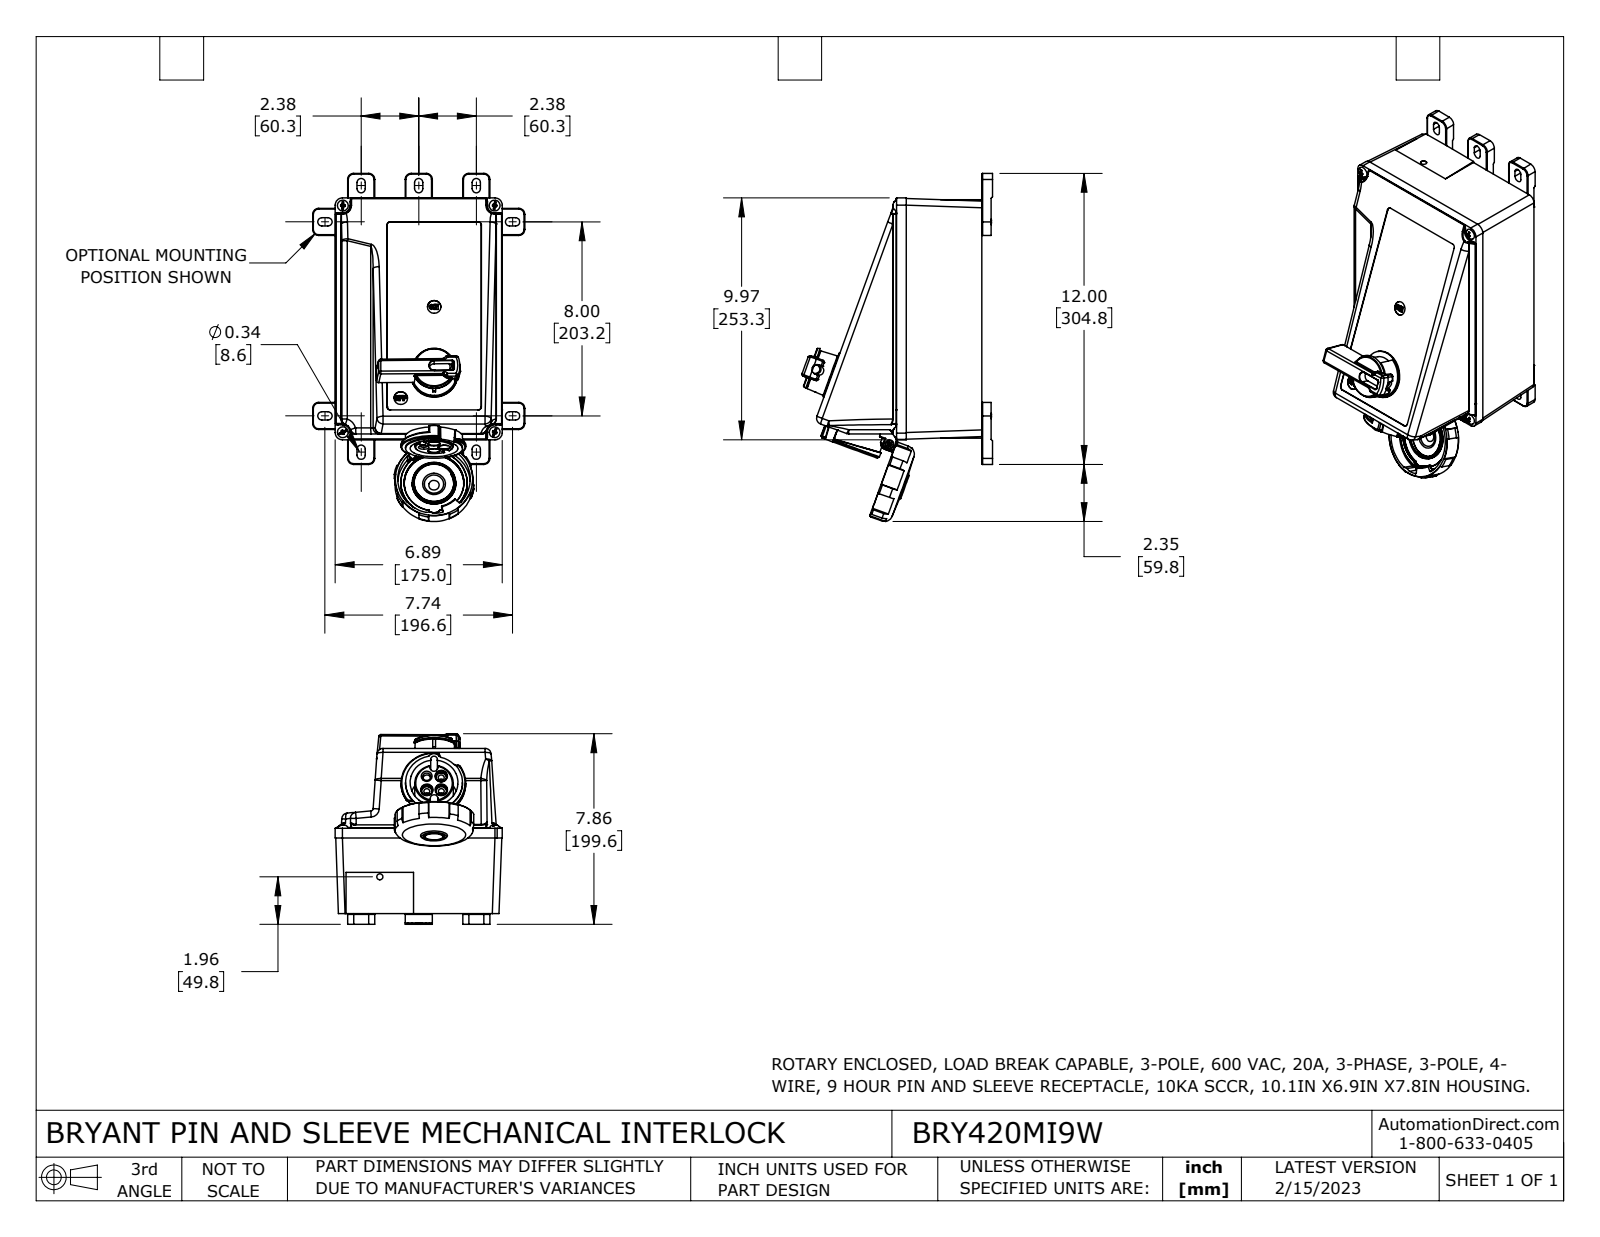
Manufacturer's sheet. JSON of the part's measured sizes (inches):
{"part_name": "BRY420MI9W", "step_written_by": "SolidWorks 2021 (CONFIG_CONTROL_DESIGN)", "units": "inches", "bodies": {"solids": 10, "faces": 2065, "planar": 740, "cylindrical": 671, "other": 654}, "overall_size": [14.354, 7.858, 6.891], "volume_in3": 334.9, "surface_area_in2": 465, "round_holes": [[0.281, 5], [0.078, 4], [0.248, 3], [0.157, 2], [0.56, 2], [0.101, 1], [0.139, 1], [0.159, 1], [0.25, 1], [0.27, 1], [0.327, 1], [0.66, 1]], "round_bosses_or_shafts": [[0.263, 2], [0.121, 2], [2.742, 1], [2.352, 1], [1.92, 1], [1.794, 1], [1.587, 1], [1.244, 1]], "partial_cylinders_radius": [[0.015, 124], [0.03, 54], [0.08, 30], [0.25, 24], [0.09, 17], [0.01, 16], [0.075, 12], [0.17, 10]], "face_to_face_distances": [0.12, 9.655, 4.75, 9.83, 0.175, 4.168, 4.156, 0.15, 0.38, 0.035], "hole_center_spacings": [0.7, 0.423, 0.598, 0.476, 1.014, 0.422, 0.424, 0.7]}
